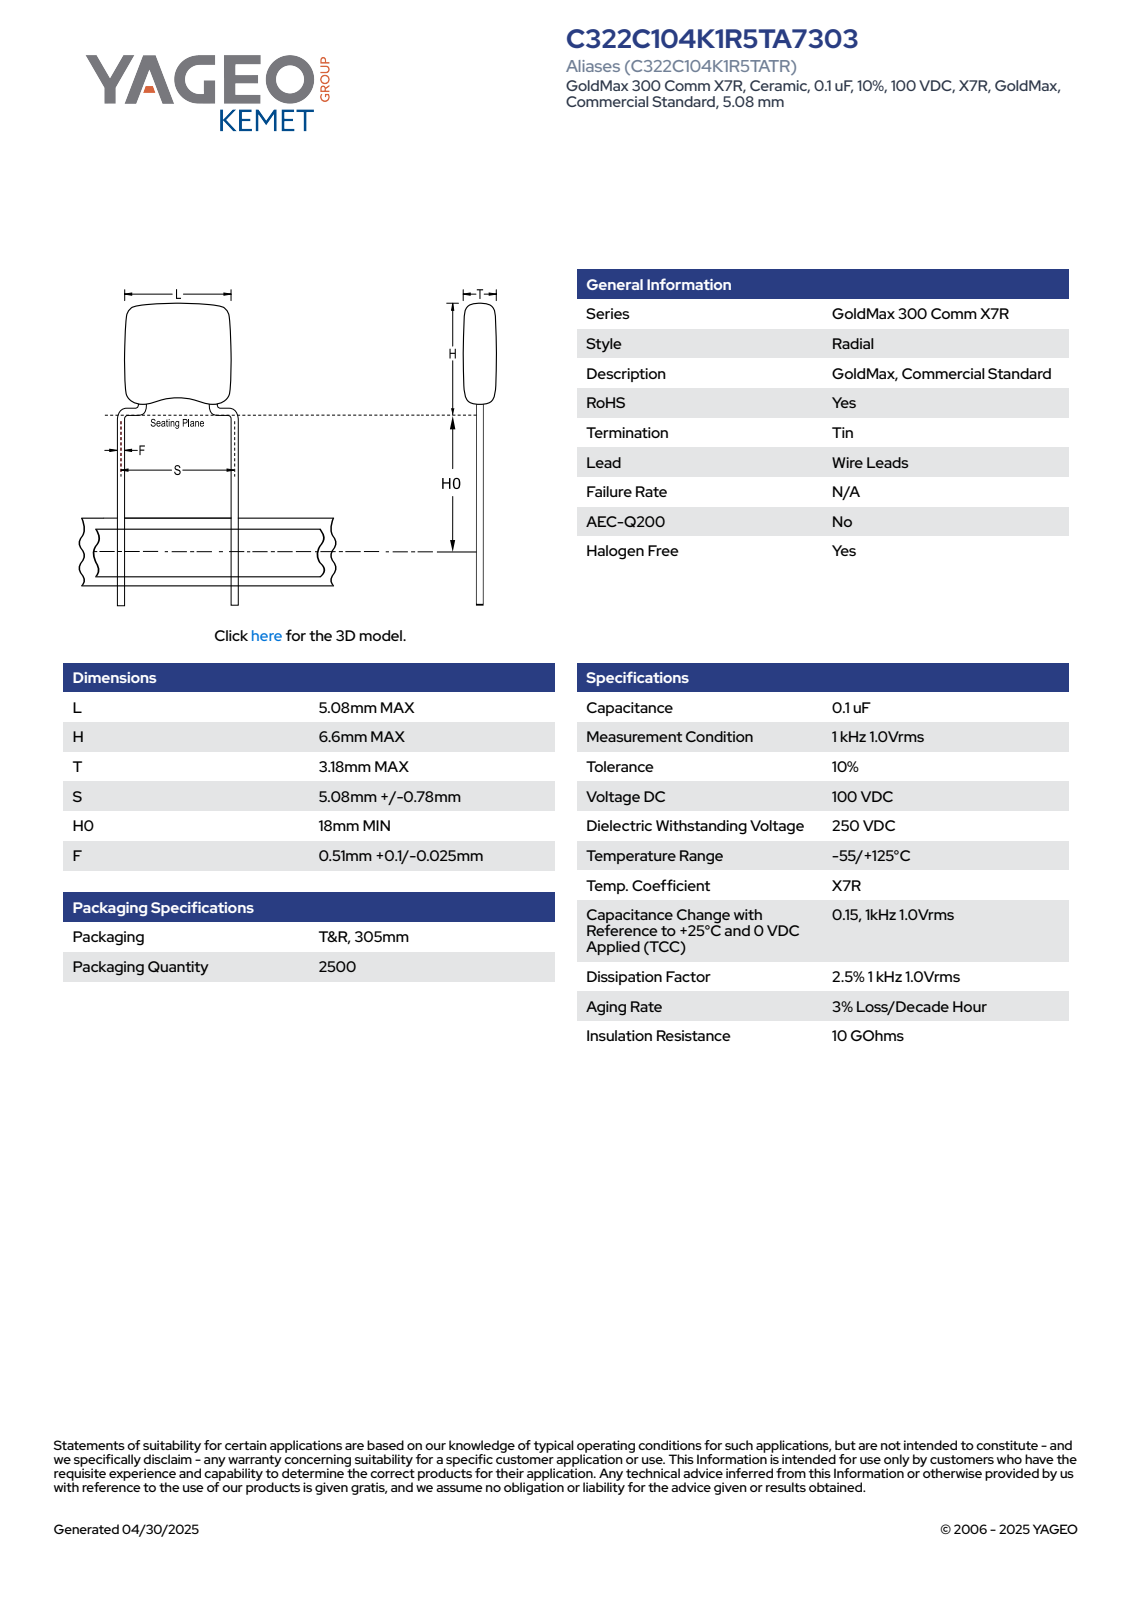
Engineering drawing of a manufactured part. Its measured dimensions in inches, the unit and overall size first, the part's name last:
Units: inches
Overall size (bounding box): 0.969 × 0.22 × 0.126
Round bosses / shafts (diameter × count): ⌀0.02 ×2
Partial cylindrical surfaces — rounded edges, fillets, slot ends (radius × count): R0.039 ×10
Main face-to-face distances: 0.125, 0.2, 0.189, 0.126, 0.017, 0.102, 0.087, 0.085, 0.104, 0.015
Volume: 0.005 in³ · Surface area: 0.245 in²
Bodies: 4 solids, 97 faces (65 planar, 14 cylindrical, 18 other)
Part name (STEP PRODUCT): CCR_SB_5.08X6.6_L5.08H6.6T3.18S5.08H018F0.51
STEP written by: SolidWorks 2014 (AUTOMOTIVE_DESIGN)
